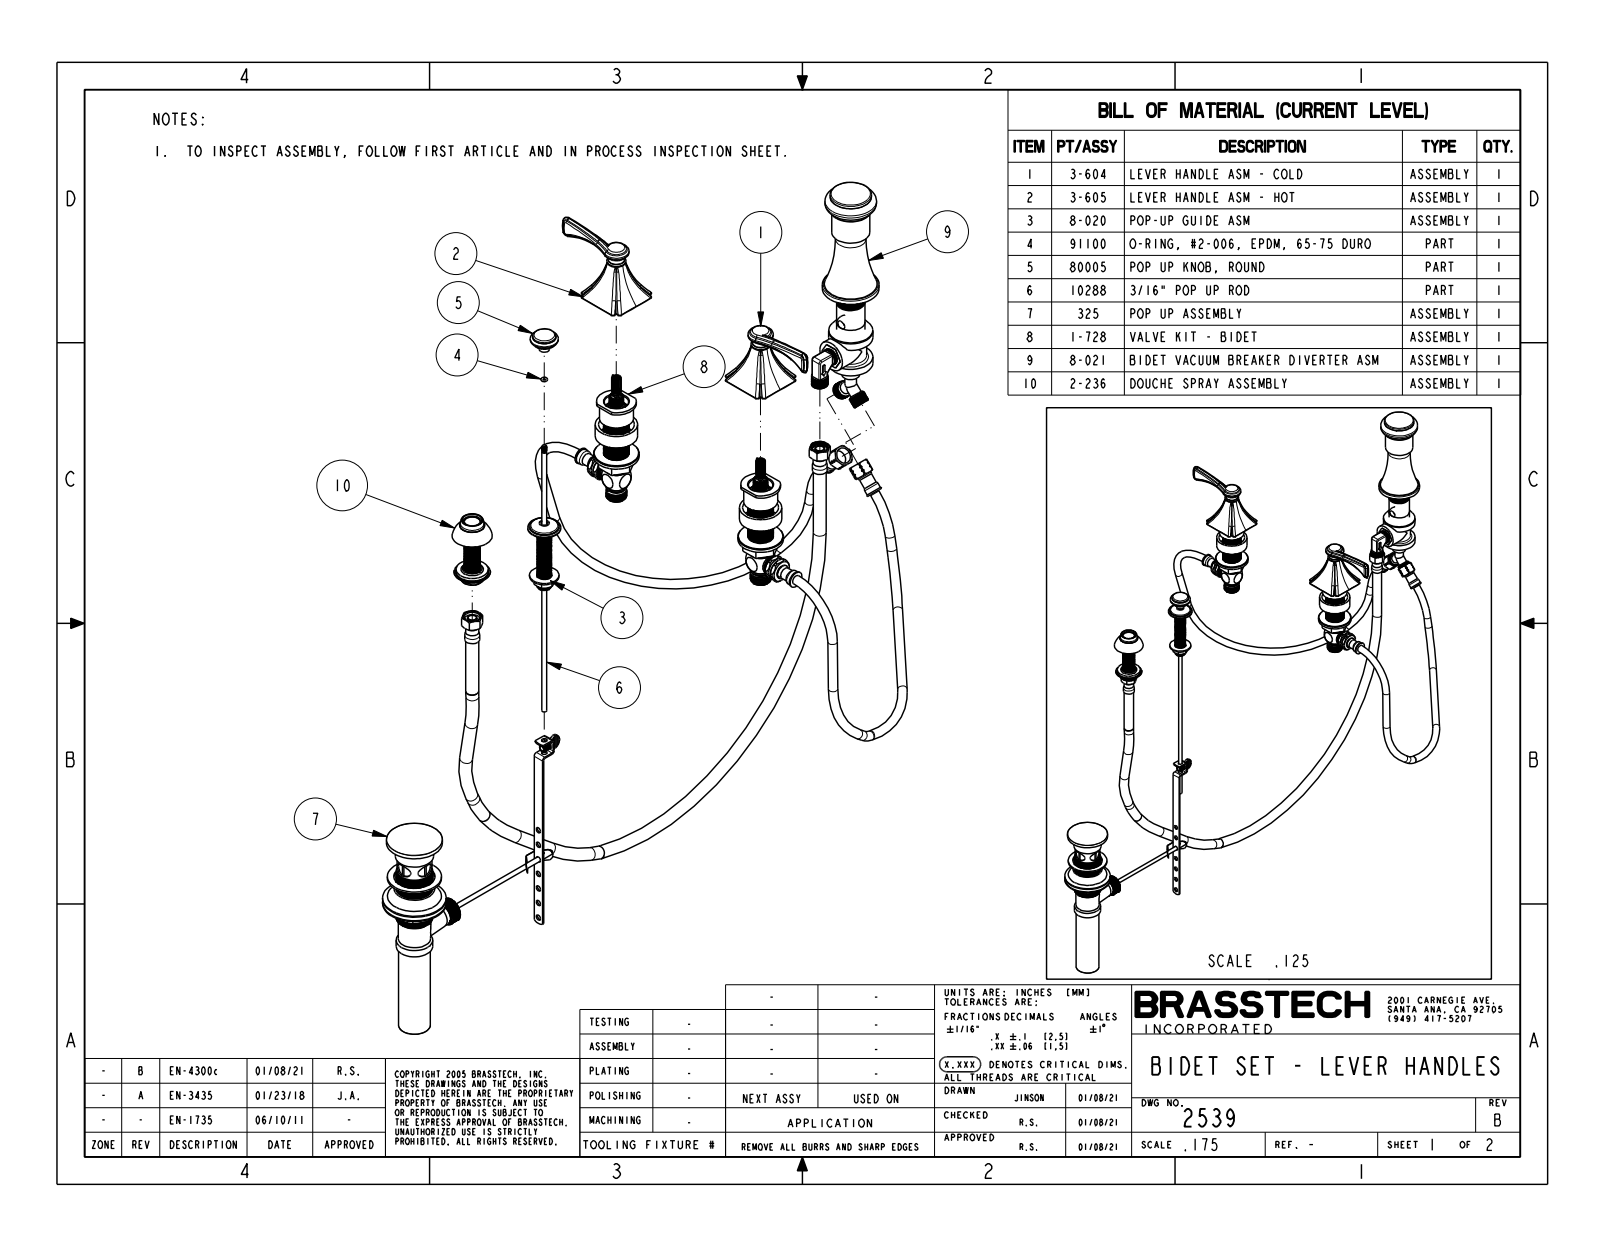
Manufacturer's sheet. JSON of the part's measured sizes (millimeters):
{"part_name": "2539", "step_written_by": "CREO PARAMETRIC BY PTC INC, 2018400 (CONFIG_CONTROL_DESIGN)", "units": "millimeters", "bodies": {"solids": 5, "faces": 491, "planar": 59, "cylindrical": 64, "other": 368}, "overall_size": [581.8, 343.6, 115.6], "volume_mm3": 281900, "surface_area_mm2": 54930, "round_holes": [[15.9, 1], [20.1, 1], [23.9, 1]], "round_bosses_or_shafts": [[52.1, 2], [16, 2], [12.9, 2], [56.6, 1], [51.3, 1], [41.1, 1], [38.1, 1], [33, 1]], "partial_cylinders_radius": [[1, 2], [12.5, 2], [98.1, 2], [104.4, 2], [106.6, 2], [9.1, 1]], "face_to_face_distances": [115.6, 115.3, 59.1, 58.8, 56.5, 68.6, 68.3, 9.5, 47, 26]}
